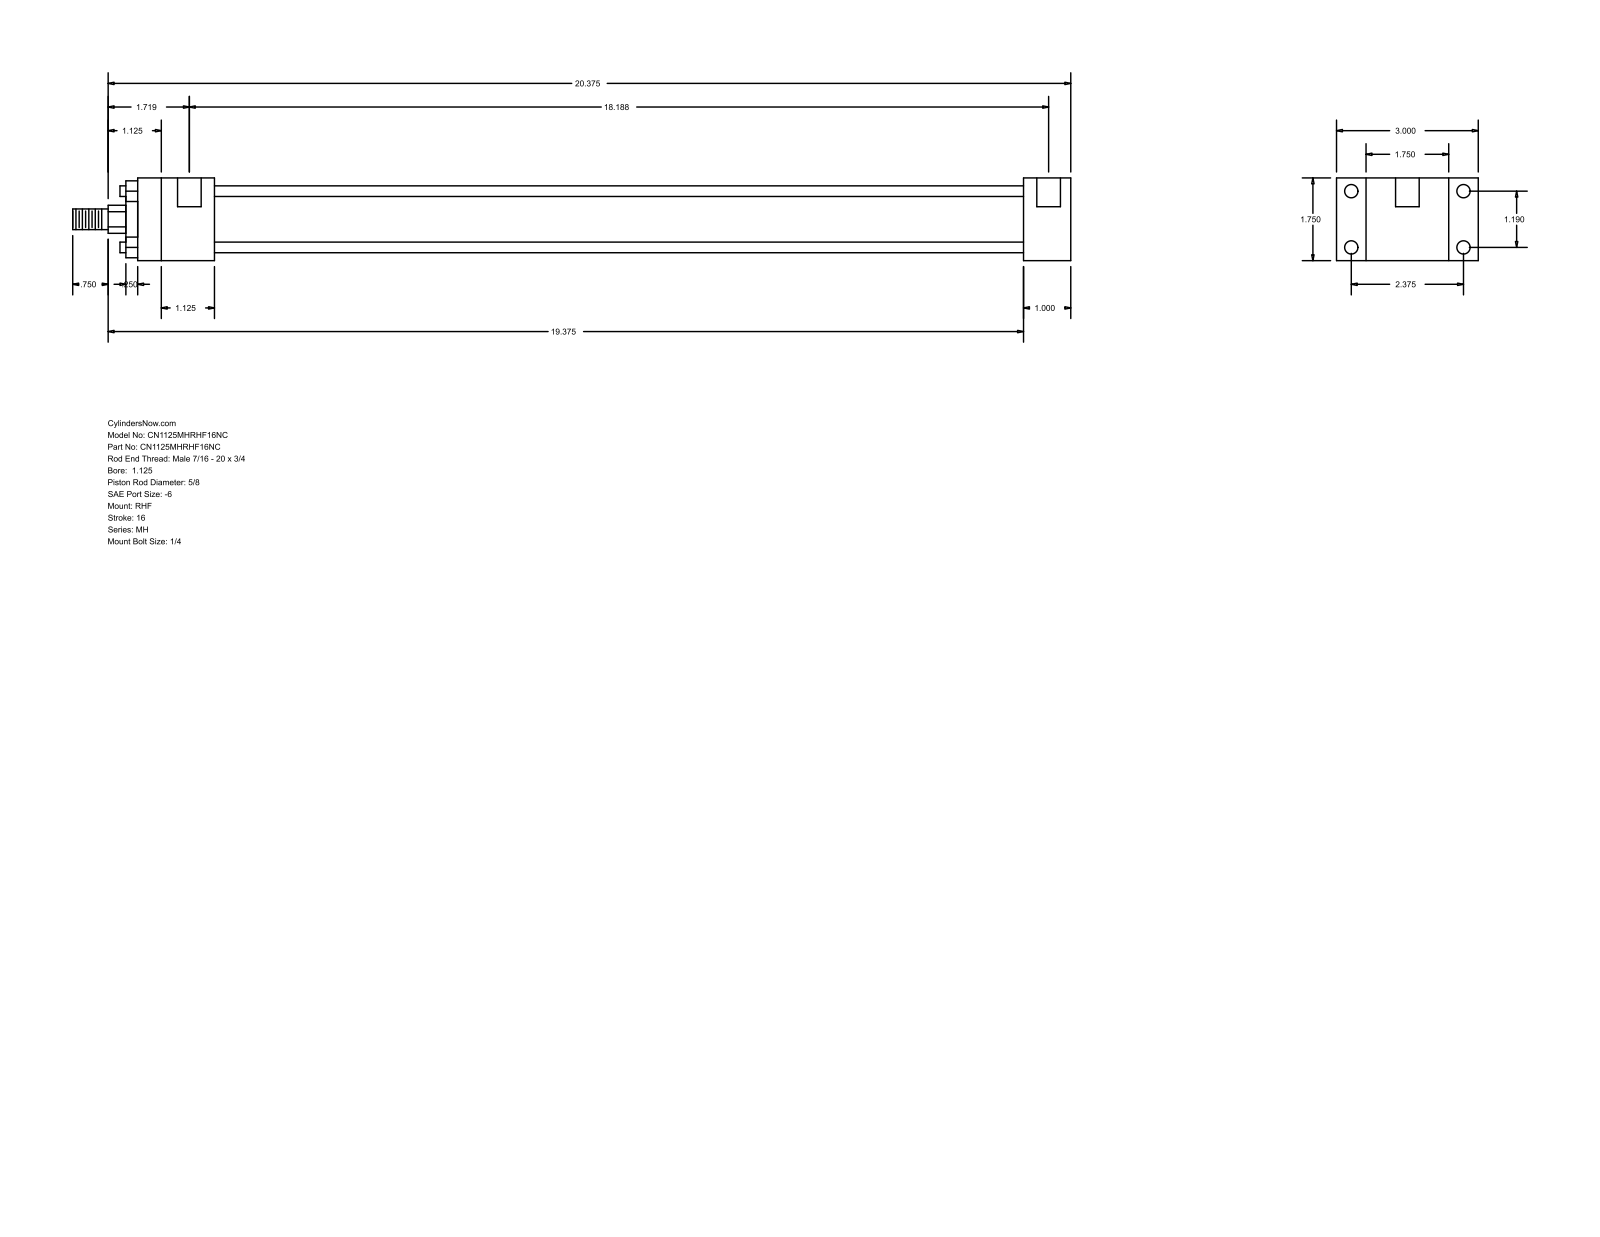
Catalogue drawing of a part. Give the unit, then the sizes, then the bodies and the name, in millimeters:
Units: millimetres
Overall size (bounding box): 536.58 × 76.2 × 44.45
Round holes (diameter × count): ⌀5.56 ×4, ⌀7.14 ×4, ⌀12.7 ×2
Round bosses / shafts (diameter × count): ⌀5.71 ×4, ⌀34.92 ×1, ⌀28.57 ×1, ⌀15.88 ×1, ⌀11.11 ×1
Partial cylindrical surfaces — rounded edges, fillets, slot ends (radius × count): R7.54 ×1
Main face-to-face distances: 44.46, 15.87, 25.4, 60.33, 76.2, 434.97, 460.37, 41.27, 476.24, 501.64
Hole centre spacings: 30.22, 60.32, 67.47, 458.79, 3.17, 461.96
Bodies: 0 solids, 88 faces (60 planar, 28 cylindrical, 0 other)
Part name (STEP PRODUCT): MH_RHF__0112_0.625
STEP written by: GSSL Pune (CONFIG_CONTROL_DESIGN)
